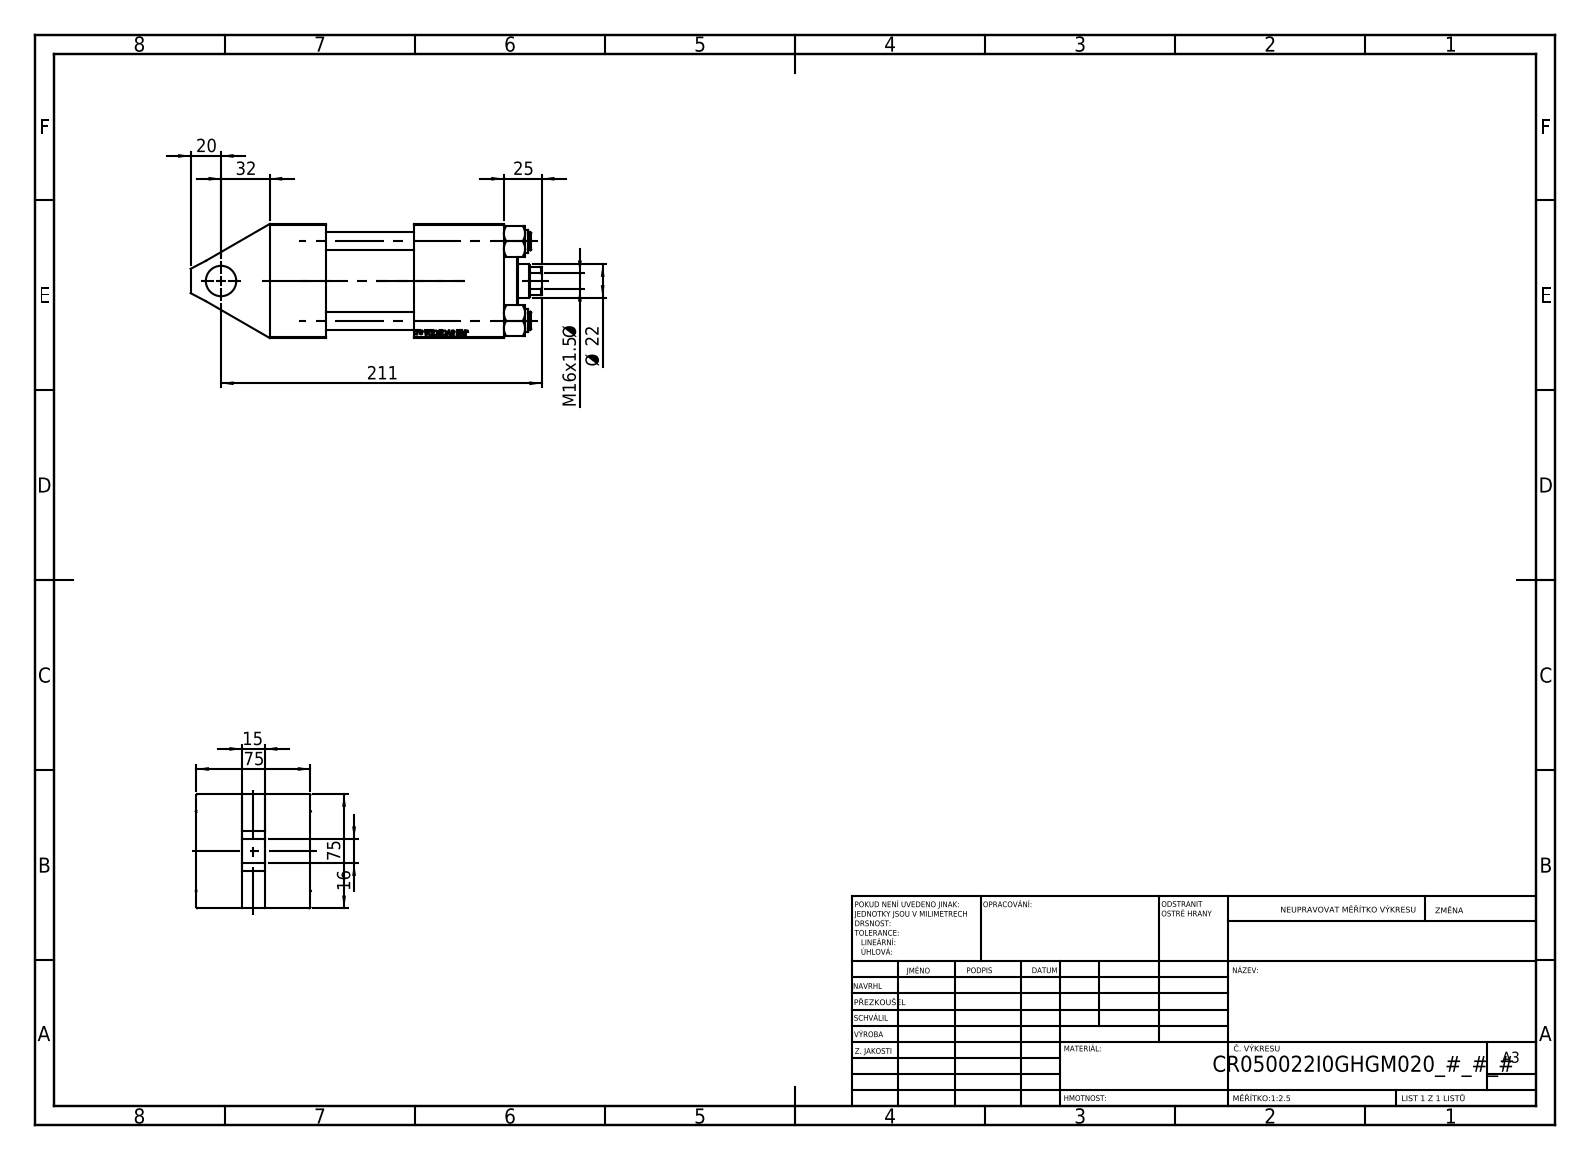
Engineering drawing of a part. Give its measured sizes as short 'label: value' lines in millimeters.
name: NUT_M5_I; V215CR_VCP_I; V215CR_TYCINKA_I; V215_VC_A (+1 more)
written by: SolidWorks 2019 (CONFIG_CONTROL_DESIGN)
unit: mm
bodies: 11 solids, 1079 faces (502 planar, 81 cylindrical, 496 other)
size: 231 × 75.54 × 75
volume: 699 574 mm³; area: 156 292 mm²
holes: 4× ⌀12, 2× ⌀7, 2× ⌀20.96, 2× ⌀30, 1× ⌀10.5, 1× ⌀20, 1× ⌀22, 1× ⌀25, 1× ⌀41, 1× ⌀50, 1× ⌀53
bosses: 4× ⌀15, 1× ⌀56, 1× ⌀34
rounds: 1× R10.5
face distances: 75, 117, 37, 154, 45, 30, 95, 58, 59, 125.3
hole spacings: 36.98, 52.3, 73.96, 50.5, 93.5, 144
